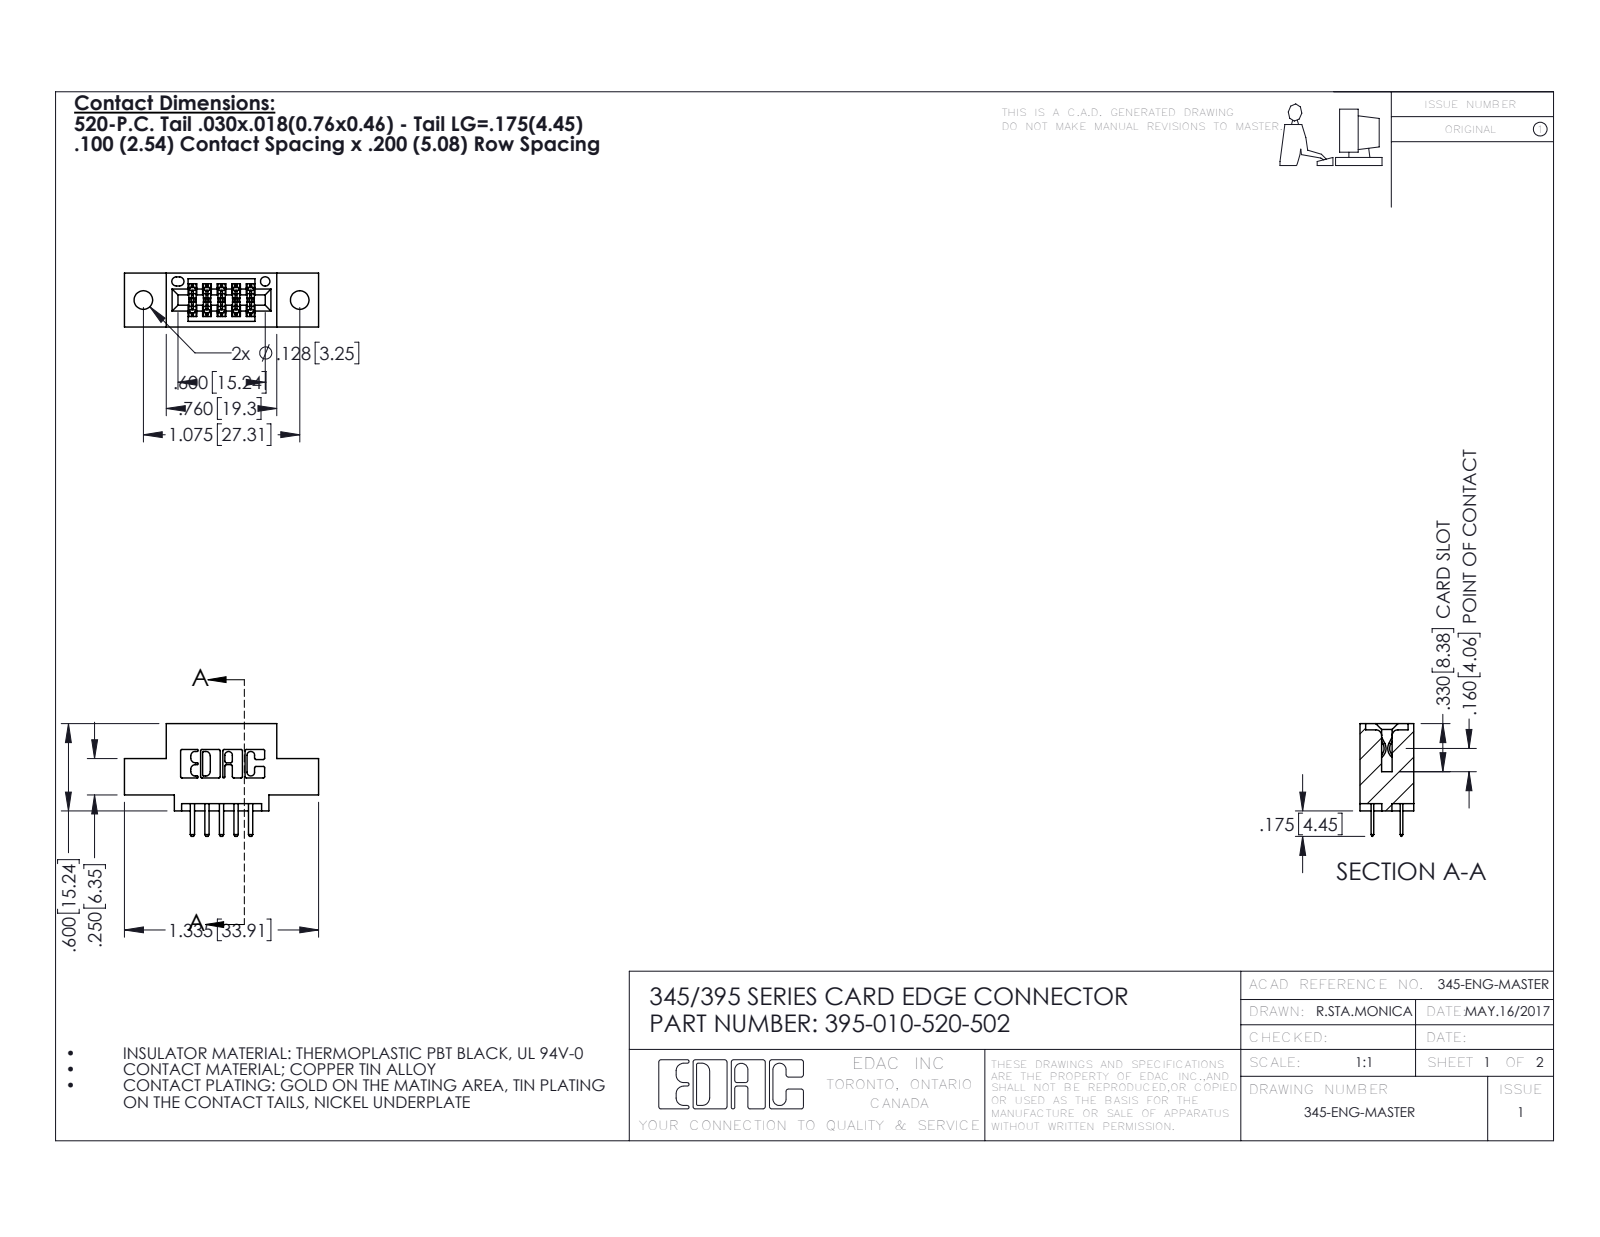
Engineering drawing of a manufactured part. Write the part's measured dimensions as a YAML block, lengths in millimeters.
part_name: "345-292-001_345-293-120; 345 Part_0.110 Offset - 0.128 Dia; 395-010-520-502"
step_written_by: "SolidWorks 2016 (CONFIG_CONTROL_DESIGN)"
units: millimeters
bodies: {solids: 11, faces: 670, planar: 434, cylindrical: 236, other: 0}
overall_size: [33.9, 19.7, 9.4]
volume: 2830
surface_area: 3286
round_holes:
  - {diameter: 3.3, count: 2}
  - {diameter: 1.6, count: 1}
partial_cylinders:
  - {radius: 0.3, count: 22}
  - {radius: 0.2, count: 15}
  - {radius: 0.3, count: 14}
  - {radius: 0.2, count: 6}
  - {radius: 0.8, count: 6}
  - {radius: 0.7, count: 3}
  - {radius: 0.4, count: 2}
  - {radius: 0.5, count: 2}
face_to_face_distances: [5.1, 9.4, 7.6, 1.8, 2.5, 6.4, 0.6, 2.5, 6.9, 1.5]
hole_center_spacings: [6.9, 21.5, 27.3]
